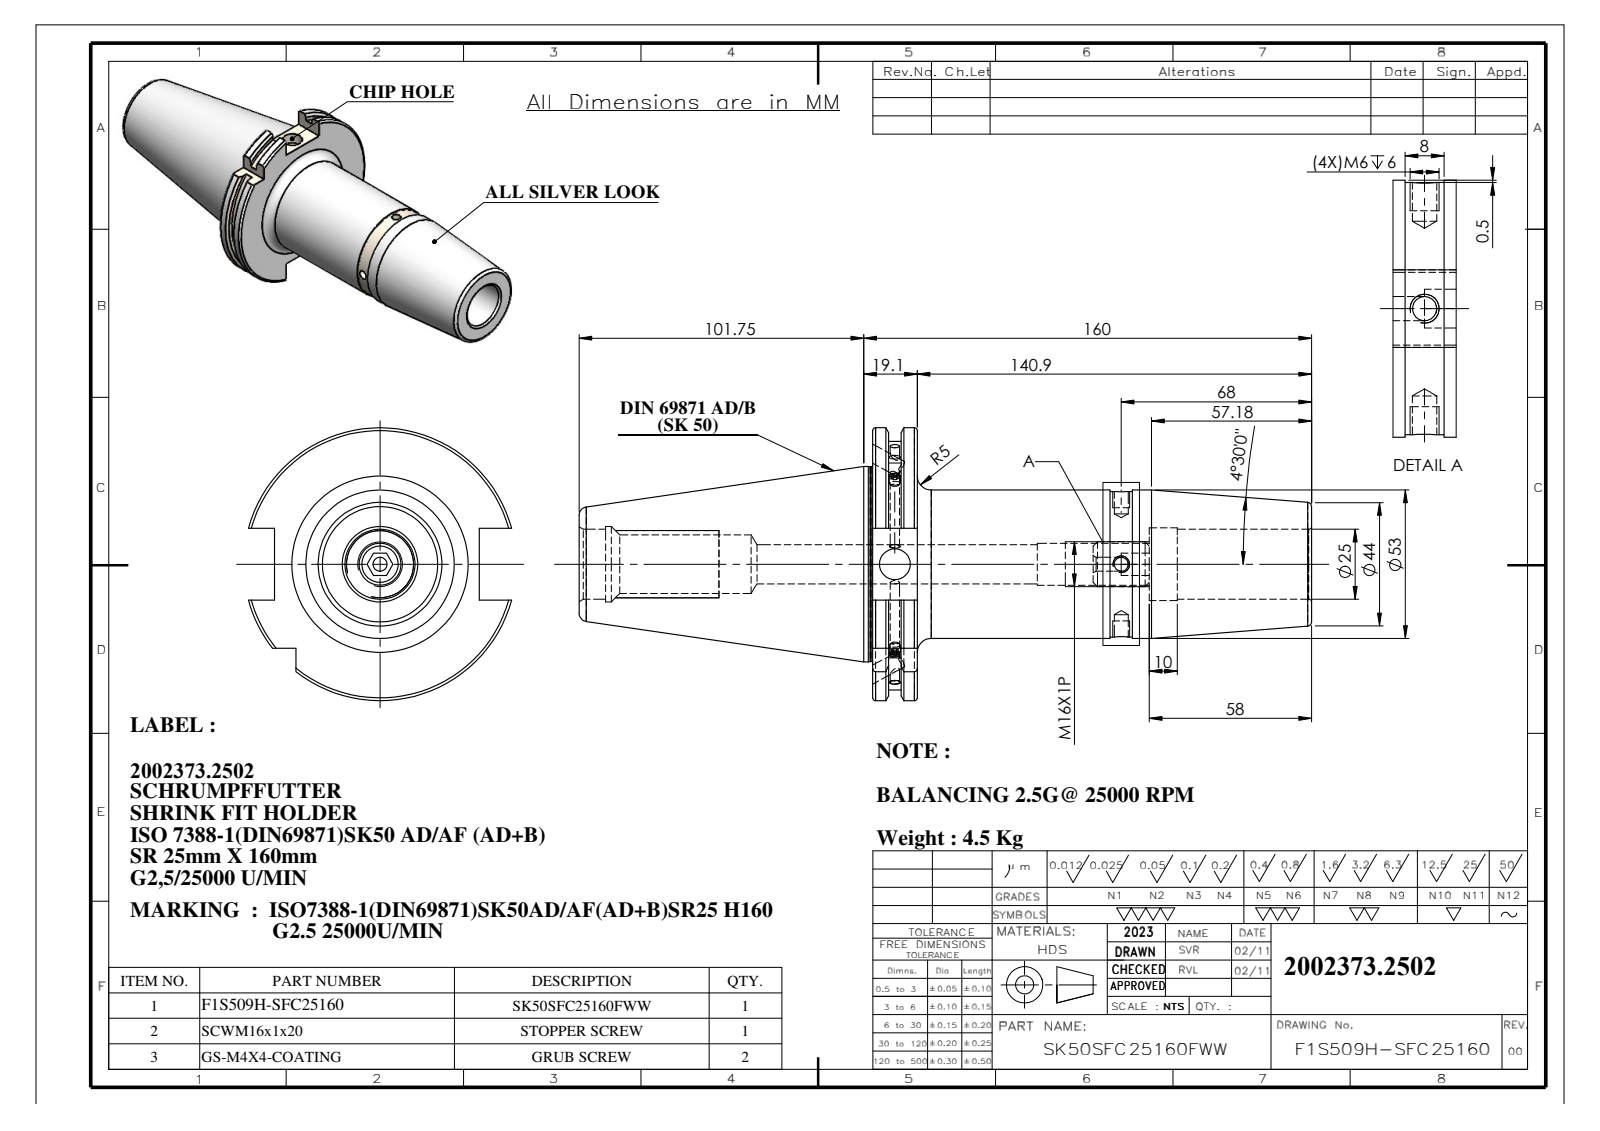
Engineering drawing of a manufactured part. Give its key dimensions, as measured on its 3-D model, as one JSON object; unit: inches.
{"part_name": "91506-SR225160", "step_written_by": "SolidWorks 2018 (AUTOMOTIVE_DESIGN)", "units": "inches", "bodies": {"solids": 1, "faces": 122, "planar": 29, "cylindrical": 53, "other": 40}, "overall_size": [10.305, 3.839, 3.703], "volume_in3": 35.74, "surface_area_in2": 113.4, "round_holes": [[0.197, 2], [0.236, 2], [0.433, 2], [0.13, 1], [0.827, 1], [0.984, 1], [0.984, 1], [1.024, 1], [1.063, 1]], "round_bosses_or_shafts": [[2.75, 1], [2.734, 1], [2.087, 1]], "partial_cylinders_radius": [[1.768, 1], [1.919, 1]], "face_to_face_distances": [0.626, 6.173, 5.547, 0.223, 0.403, 5.95, 0.399, 0.176, 0.227, 5.774], "hole_center_spacings": [3.185]}
